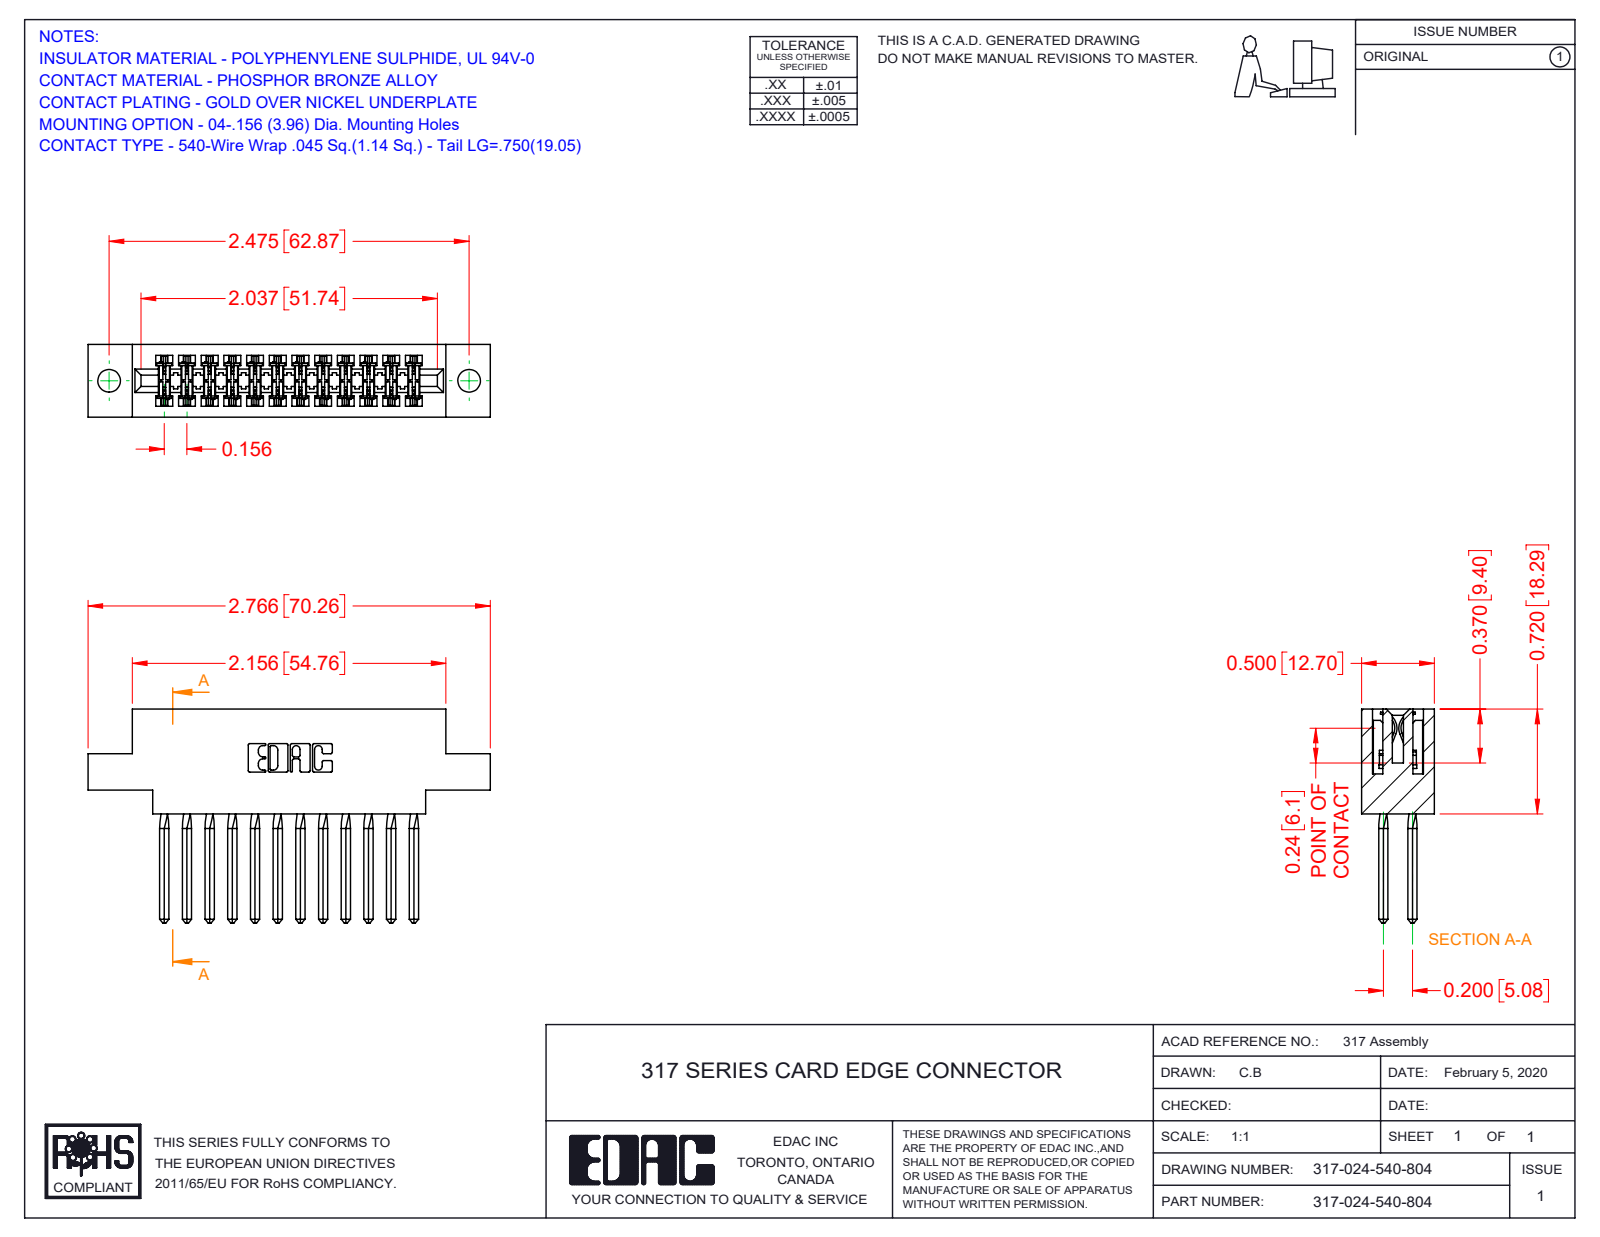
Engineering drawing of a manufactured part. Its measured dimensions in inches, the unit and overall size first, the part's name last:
Units: inches
Overall size (bounding box): 2.766 × 1.47 × 0.5
Round holes (diameter × count): ⌀0.156 ×2
Partial cylindrical surfaces — rounded edges, fillets, slot ends (radius × count): R0.015 ×48, R0.01 ×22, R0.007 ×6, R0.031 ×6, R0.026 ×3, R0.095 ×2, R0.1 ×2, R0.11 ×2
Main face-to-face distances: 0.5, 0.075, 0.425, 0.11, 0.22, 0.35, 0.331, 0.156, 0.305, 0.72
Hole centre spacings: 2.475
Volume: 0.652 in³ · Surface area: 22.67 in²
Bodies: 25 solids, 2238 faces (1810 planar, 332 cylindrical, 96 other)
Part name (STEP PRODUCT): 317 Part_.156 Dia - TH; 317-290-001_540; 317-024-540-804
STEP written by: SolidWorks 2016 (CONFIG_CONTROL_DESIGN)
